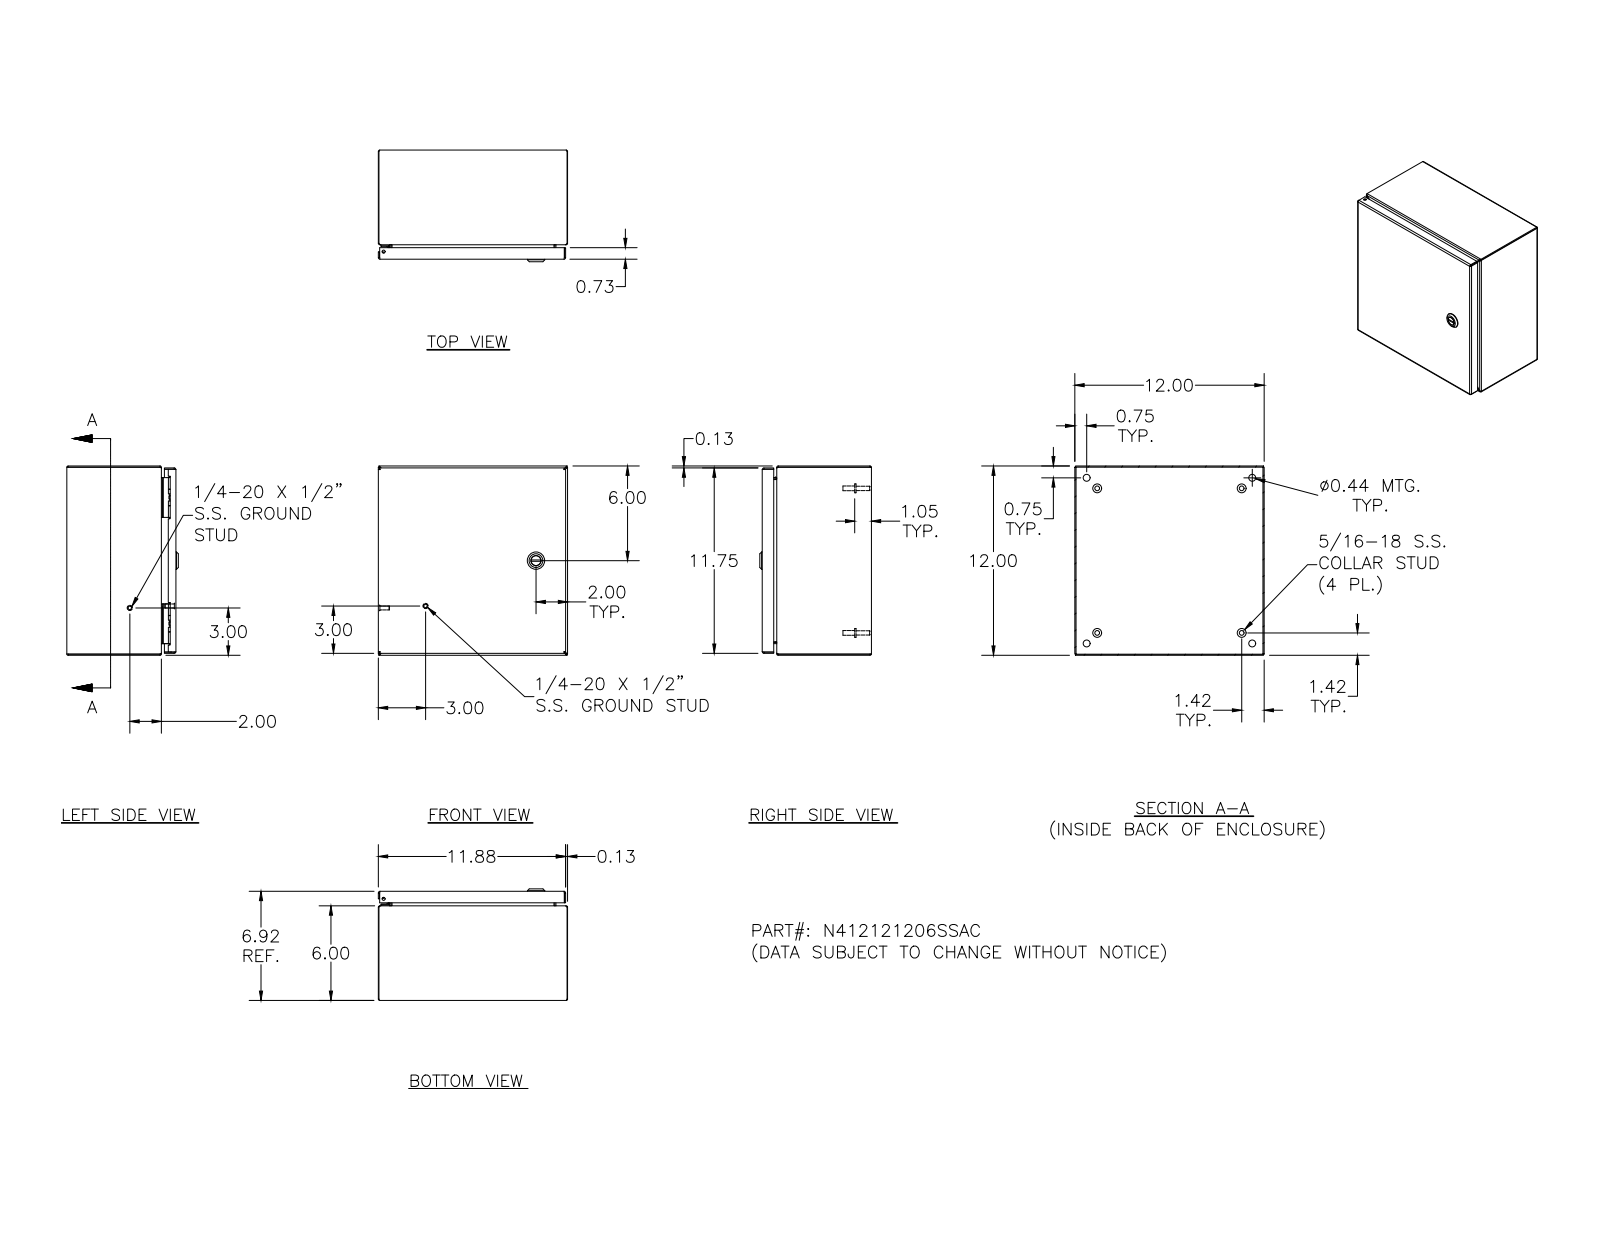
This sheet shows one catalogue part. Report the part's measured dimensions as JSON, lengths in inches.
{"part_name": "N412121206SSAC; N412121206SSACBKP; 388151; N4121212SSACLID (+8 more)", "step_written_by": "Autodesk Inventor 2011 (AUTOMOTIVE_DESIGN)", "units": "inches", "bodies": {"solids": 34, "faces": 1364, "planar": 523, "cylindrical": 497, "other": 344}, "overall_size": [12, 12, 7.075], "volume_in3": 50.63, "surface_area_in2": 1382, "round_holes": [[0.188, 5], [0.093, 4], [0.152, 4], [0.167, 4], [0.172, 4], [0.437, 4], [0.156, 2], [0.187, 1], [0.197, 1], [0.315, 1], [0.394, 1], [0.402, 1]], "round_bosses_or_shafts": [[0.25, 10], [0.563, 4], [0.36, 4], [0.32, 4], [0.3, 4], [0.275, 4], [0.256, 4], [0.164, 4]], "partial_cylinders_radius": [[0.05, 26], [0.016, 18], [0.016, 16], [0.09, 16], [0.031, 14], [0.125, 14], [0.02, 9], [0.032, 8]], "face_to_face_distances": [0.074, 11.926, 6.843, 11.852, 12, 6.769, 6.917, 5.926, 0.917, 0.739], "hole_center_spacings": [8, 0.017, 0.66, 10.5, 0.019, 0.5, 0.648, 0.652]}
